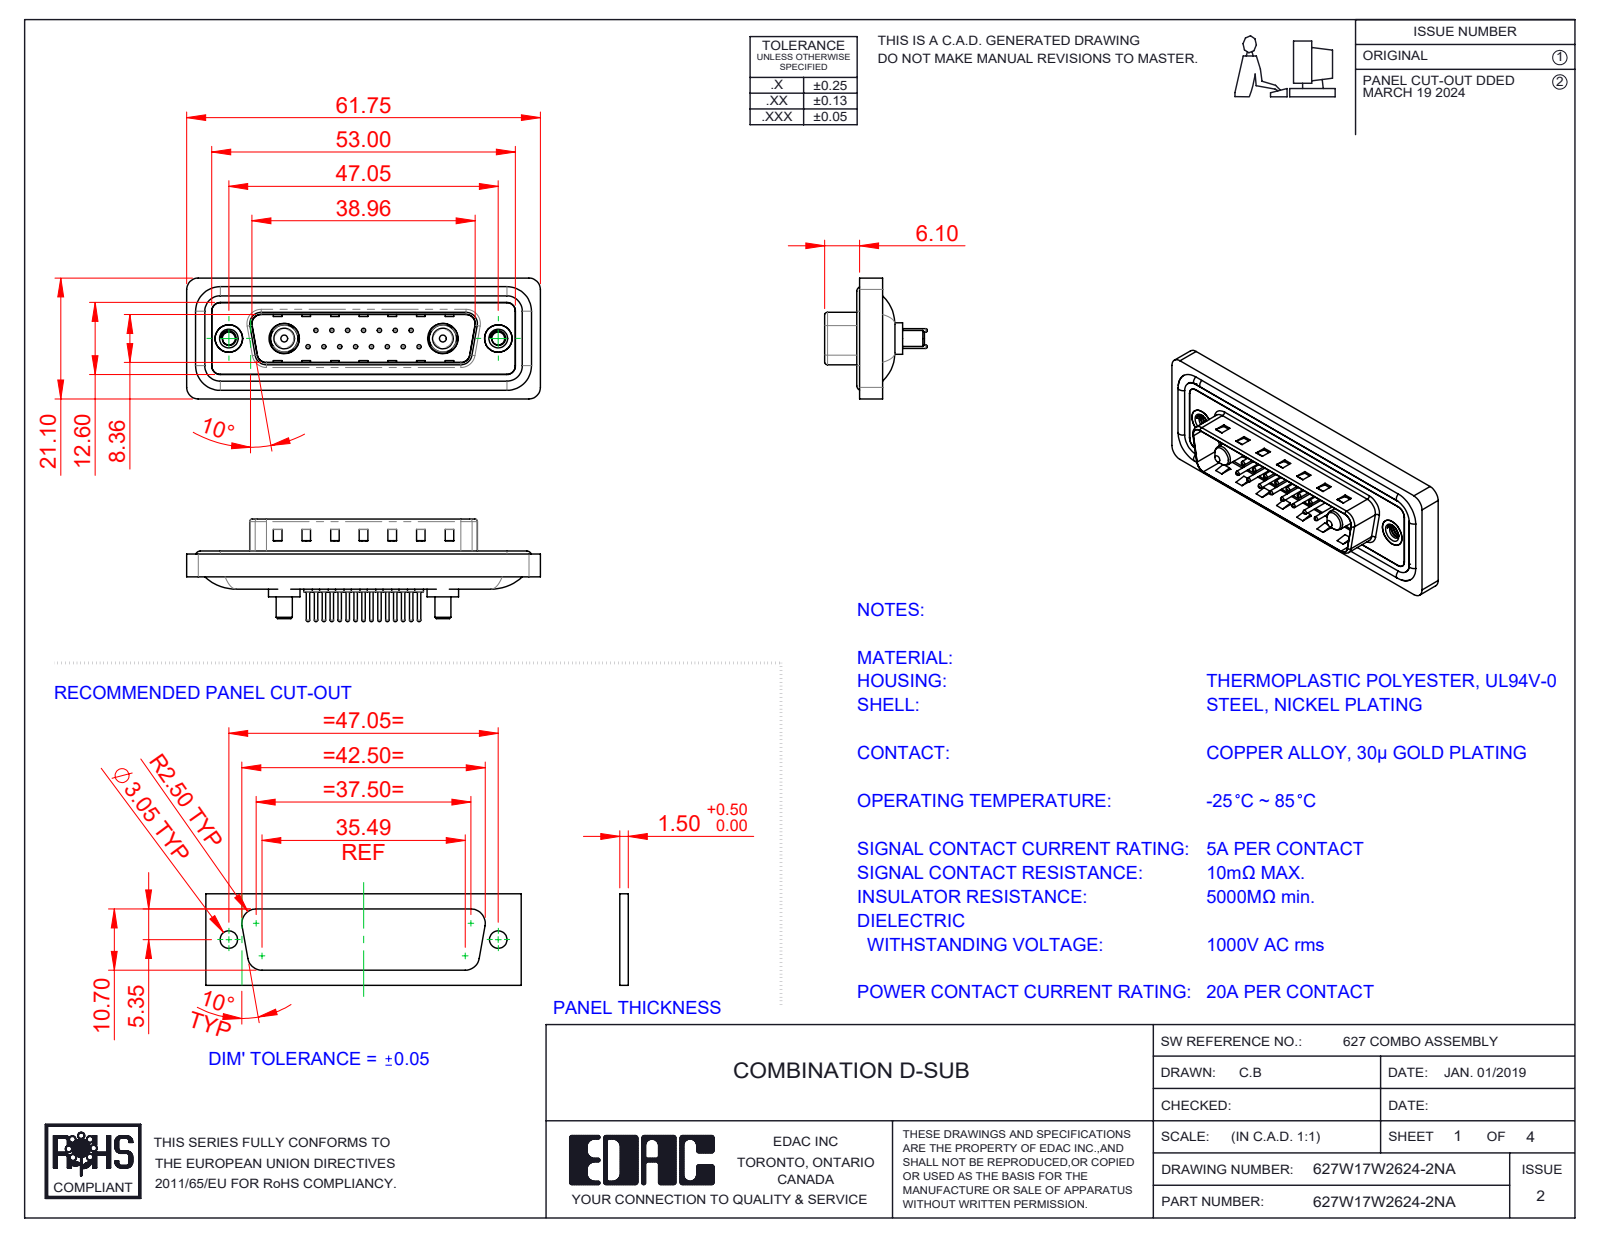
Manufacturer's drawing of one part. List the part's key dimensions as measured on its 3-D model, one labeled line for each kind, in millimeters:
Part name (STEP PRODUCT): 627Combo Shell Front_25 Contacts; 627Combo Threaded Rivet_A; 627Combo Waterproof Housing_25 Contacts; 627Combo Contact Row 1_24 (+5 more)
STEP written by: SolidWorks 2023 (CONFIG_CONTROL_DESIGN)
Units: millimetres
Bodies: 26 solids, 1114 faces (334 planar, 438 cylindrical, 342 other)
Overall size (bounding box): 61.75 × 21.1 × 17.9
Volume: 7 268 mm³ · Surface area: 11 912 mm²
Round holes (diameter × count): ⌀0.75 ×15, ⌀1.6 ×15, ⌀2 ×15, ⌀2.26 ×2, ⌀4 ×2, ⌀4.8 ×2, ⌀4.85 ×2, ⌀5 ×2, ⌀5.3 ×2
Round bosses / shafts (diameter × count): ⌀1.5 ×15, ⌀0.6 ×15, ⌀1.6 ×4, ⌀5.5 ×2, ⌀5.2 ×2, ⌀4.9 ×2, ⌀4.75 ×2, ⌀3.75 ×2
Partial cylindrical surfaces — rounded edges, fillets, slot ends (radius × count): R1.5 ×22, R2 ×18, R0.5 ×8, R1.6 ×8, R0.25 ×4, R0.6 ×4, R0.65 ×4, R0.9 ×4
Main face-to-face distances: 0.4, 1.5, 1.1, 1.6, 0.5, 3.1, 2.9, 0.82, 9.58, 4.1
Hole centre spacings: 3.16, 2.77, 5.54, 8.31, 5.04, 7.49, 11.08, 5.03
